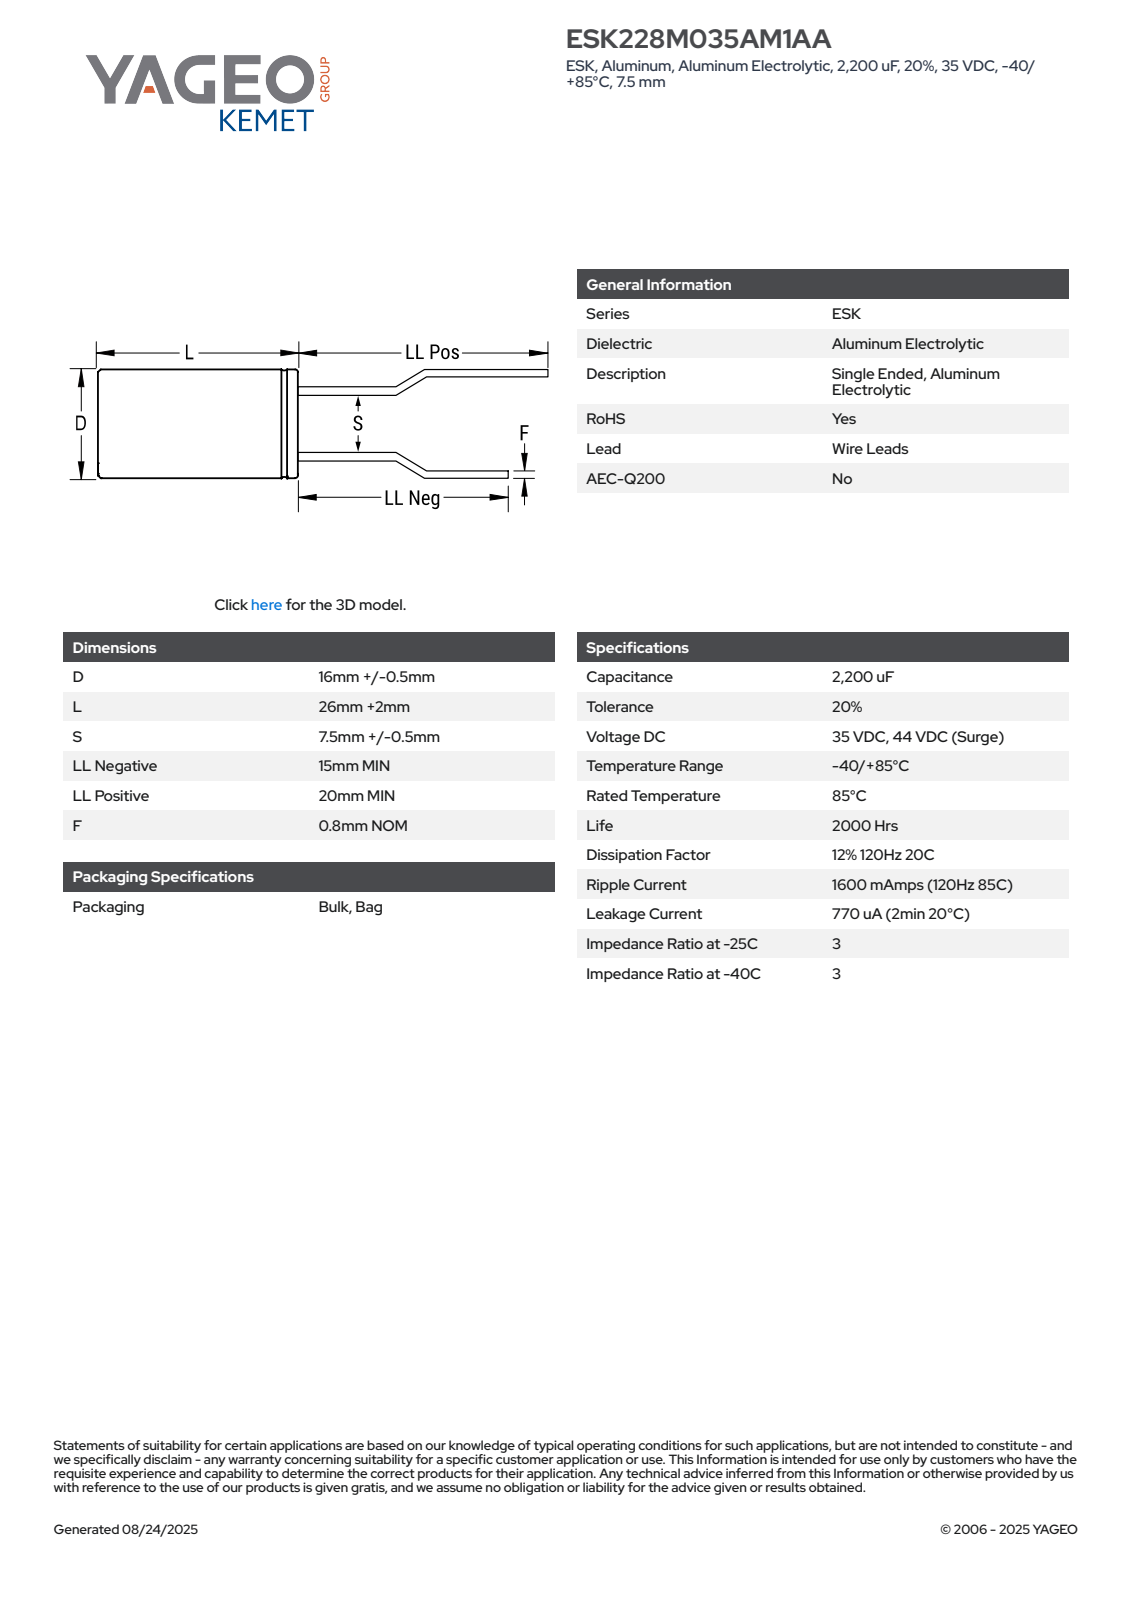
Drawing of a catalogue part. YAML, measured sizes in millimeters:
part_name: "CAR_KTRS_16X26_D16.5L28S7.5F0.8"
step_written_by: "SolidWorks 2014 (AUTOMOTIVE_DESIGN)"
units: millimeters
bodies: {solids: 4, faces: 73, planar: 61, cylindrical: 8, other: 4}
overall_size: [48.01, 16.5, 16.5]
volume: 5958
surface_area: 2028
round_bosses_or_shafts:
  - {diameter: 0.8, count: 2}
  - {diameter: 16.5, count: 1}
face_to_face_distances: [28, 28.01, 43.01, 48.01, 43, 48, 15, 20, 5, 1.96]
